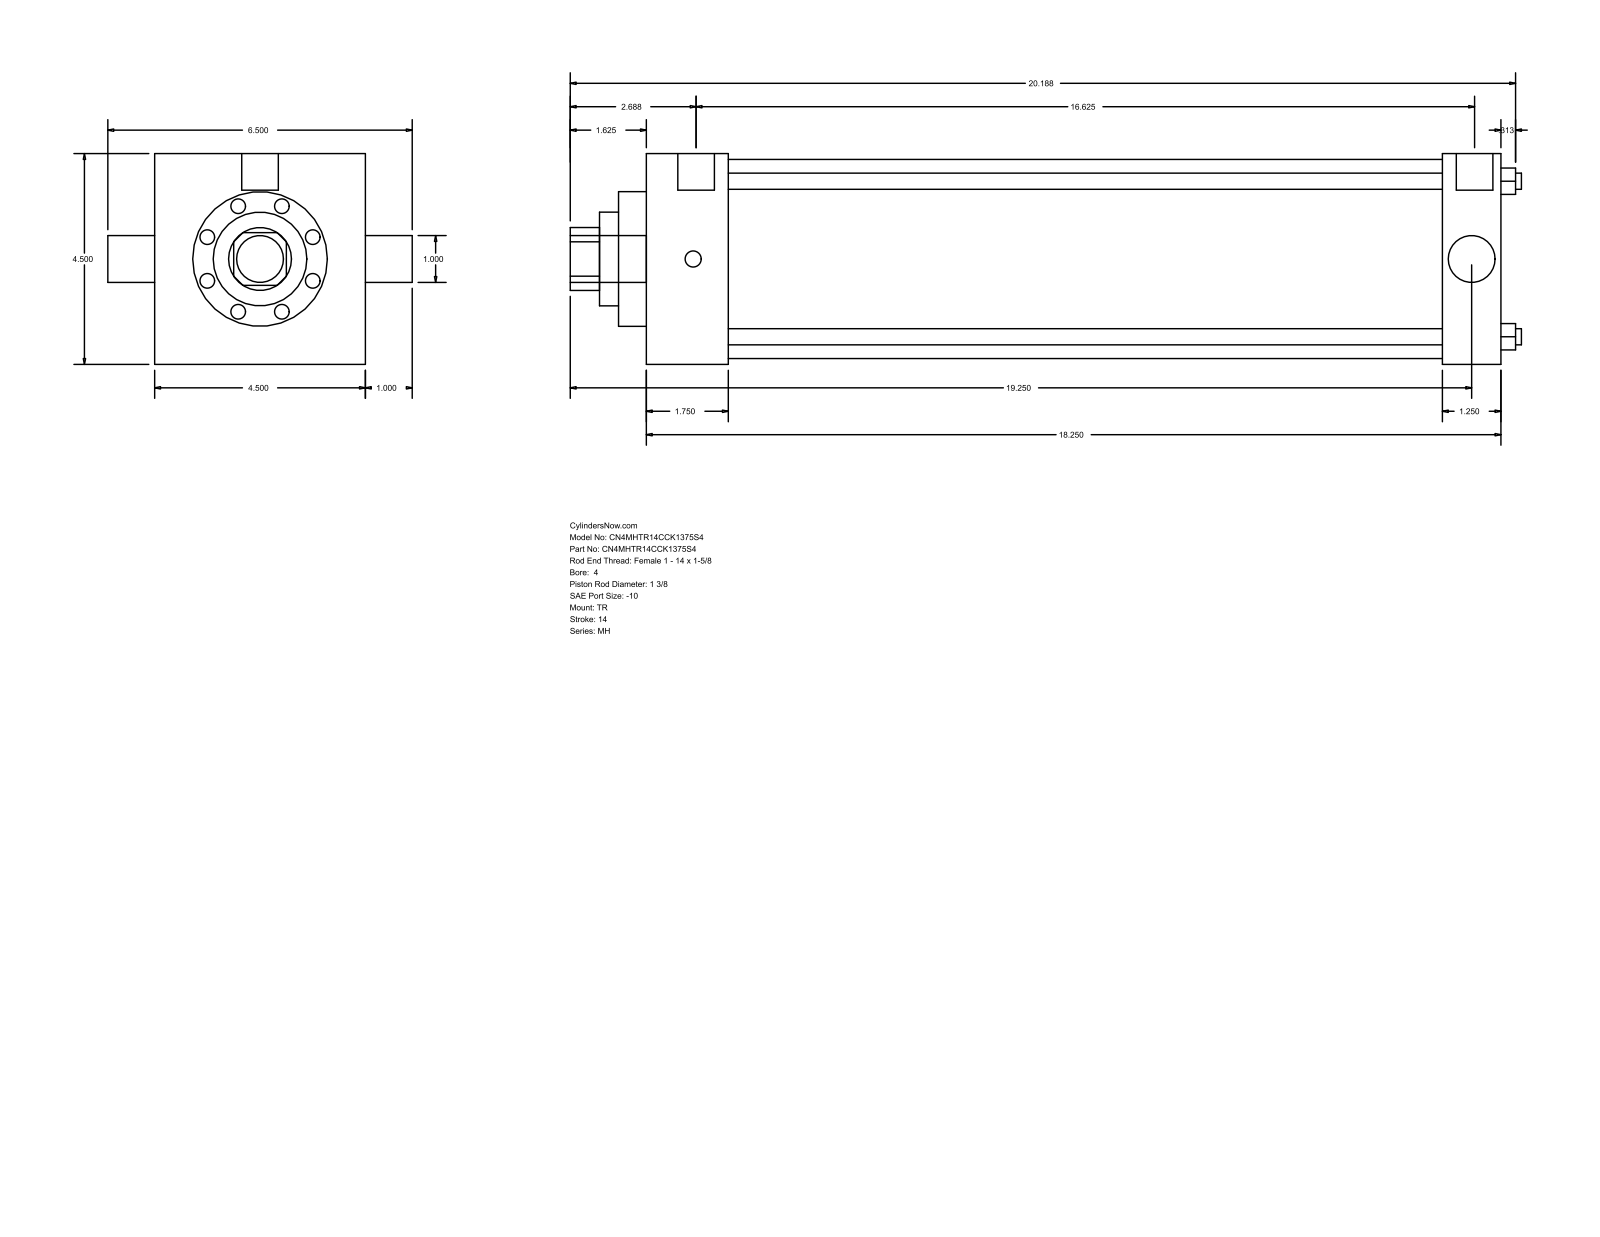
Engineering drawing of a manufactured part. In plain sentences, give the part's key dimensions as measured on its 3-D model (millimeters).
The part is named "MH_TR__0400_1.375". Its 3-D file was written by "GSSL Pune (CONFIG_CONTROL_DESIGN)". It is 0 solids with 86 faces: 61 planar, 25 cylindrical and 0 other. Overall it measures 515.94 by 165.1 by 114.3 millimeters. Round holes: 4 of diameter 8.76, 1 of diameter 25.4, 1 of diameter 34.92, 1 of diameter 50.8, 1 of diameter 73.03, 1 of diameter 107.95. Round bosses or shafts: 3 of diameter 8.73, 2 of diameter 19.84, 1 of diameter 25.4. Partial cylindrical surfaces (rounded edges, fillets, slot ends): 1 of radius 17.06. The main face-to-face distances are 114.3, 463.55, 44.45, 419.1, 431.8, 387.35, 31.75, 15.08, 59.53, 446.88. The hole center spacings are 59.62, 84.32, 119.25.
